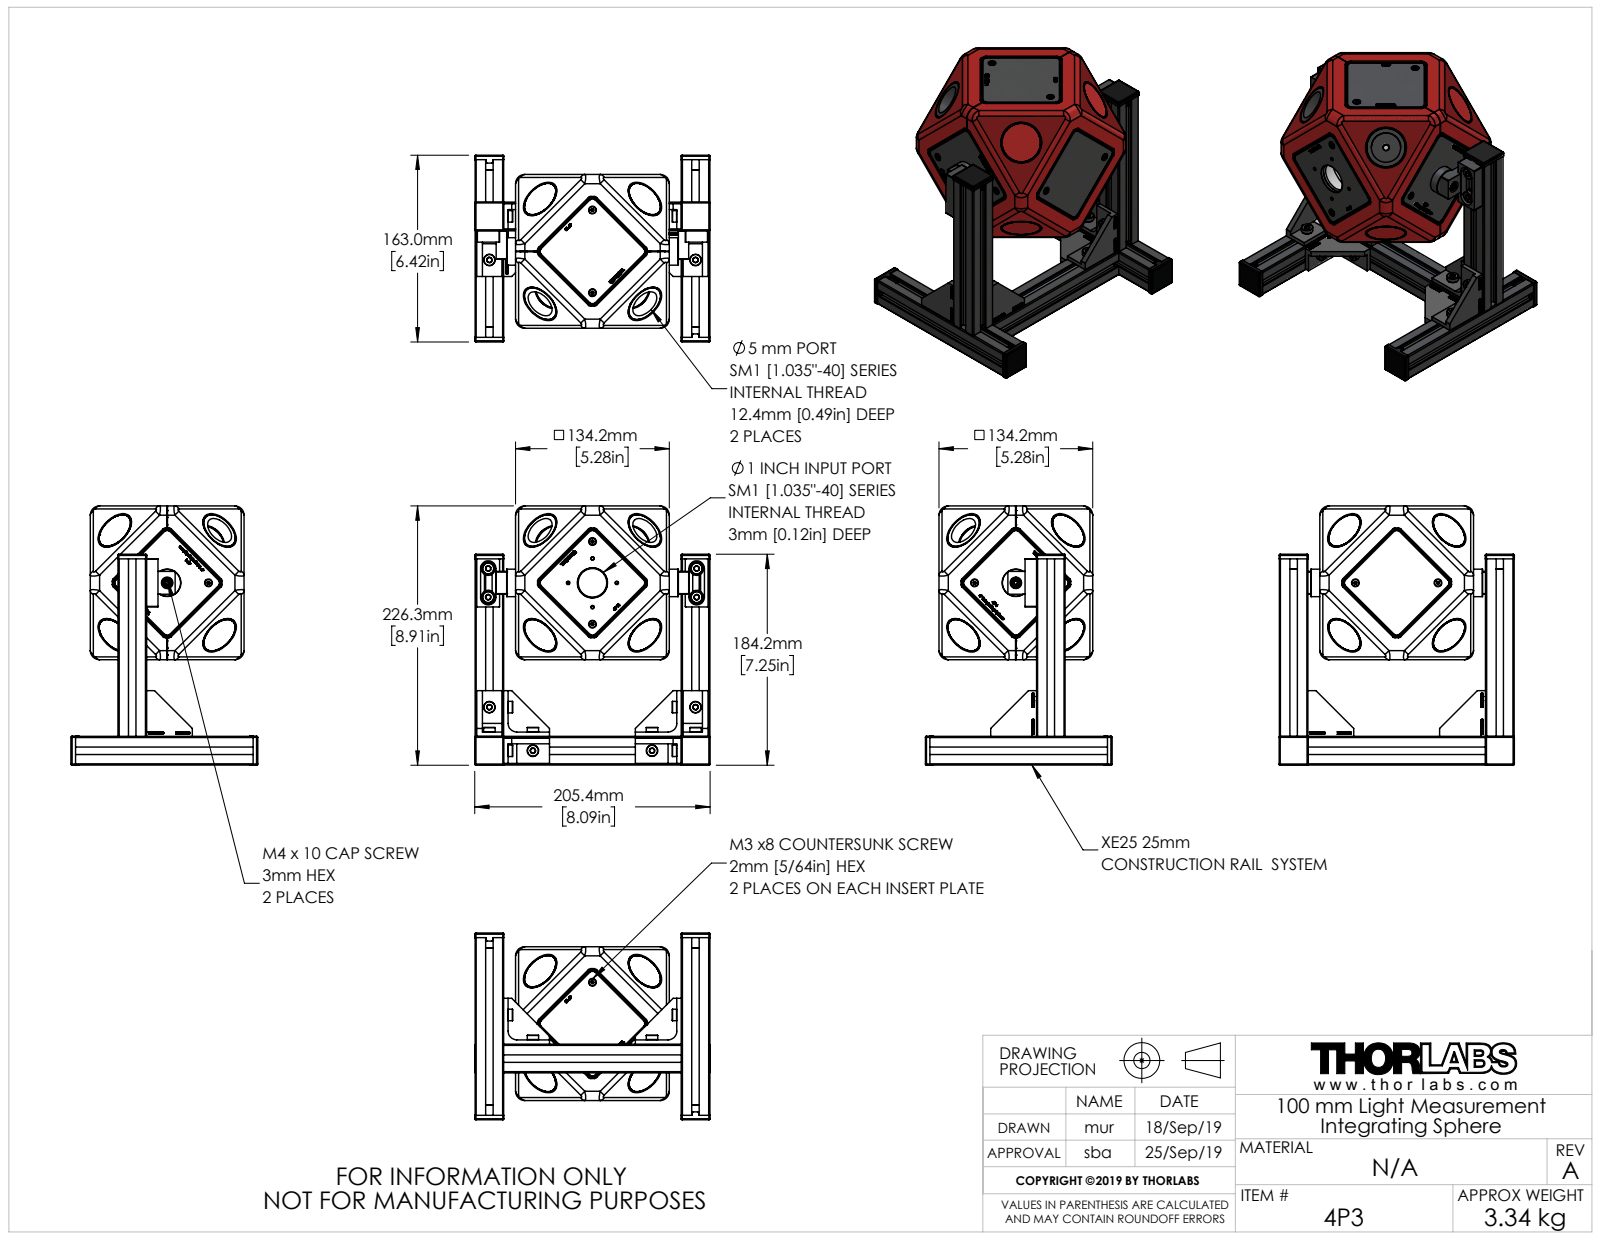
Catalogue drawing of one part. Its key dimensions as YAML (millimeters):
part_name: "19.11.08_4P3_Four Inch IS PM Config WEB"
step_written_by: "SolidWorks 2018 (AUTOMOTIVE_DESIGN)"
units: millimeters
bodies: {solids: 0, faces: 9872, planar: 5569, cylindrical: 1787, other: 2516}
overall_size: [226.3, 205.39, 163]
round_holes:
  - {diameter: 4.04, count: 20}
  - {diameter: 5, count: 19}
  - {diameter: 4, count: 12}
  - {diameter: 5.5, count: 12}
  - {diameter: 4.5, count: 9}
  - {diameter: 6.5, count: 9}
  - {diameter: 2.5, count: 8}
  - {diameter: 3.2, count: 8}
  - {diameter: 30.5, count: 8}
  - {diameter: 32.3, count: 8}
  - {diameter: 34.8, count: 8}
  - {diameter: 2.26, count: 4}
round_bosses_or_shafts:
  - {diameter: 10, count: 14}
  - {diameter: 6, count: 14}
  - {diameter: 34, count: 8}
  - {diameter: 32, count: 8}
  - {diameter: 5.7, count: 8}
  - {diameter: 3, count: 8}
  - {diameter: 34.1, count: 6}
  - {diameter: 12, count: 4}
partial_cylinders:
  - {radius: 0.2, count: 300}
  - {radius: 1, count: 234}
  - {radius: 0.5, count: 68}
  - {radius: 0.25, count: 64}
  - {radius: 2, count: 56}
  - {radius: 6, count: 36}
  - {radius: 0.8, count: 32}
  - {radius: 2.5, count: 24}
face_to_face_distances: [3, 131, 128, 3.1, 131.1, 134.1, 17.9, 118.2, 8, 25]
hole_center_spacings: [30.7, 12.02, 17, 47.27, 38, 12.01, 16.99, 24.03]
